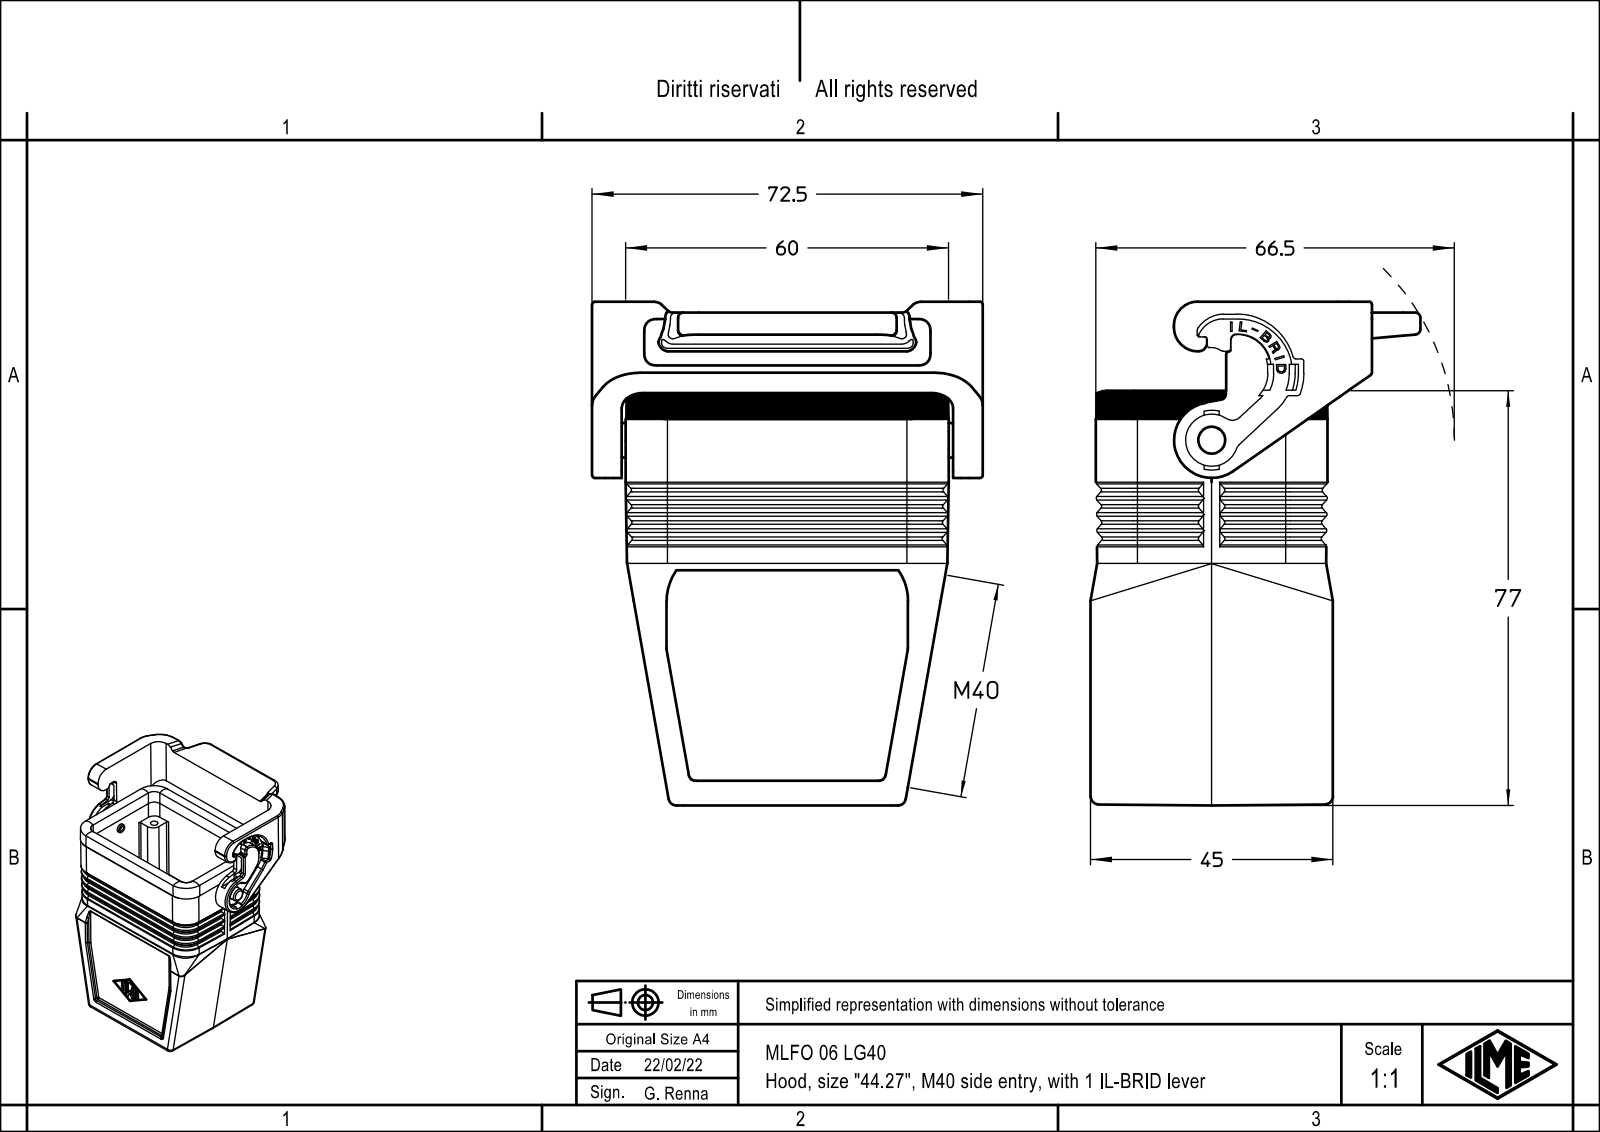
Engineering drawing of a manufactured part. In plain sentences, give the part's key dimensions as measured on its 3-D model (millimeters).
The part is named "MLFO_06_LG40". Its 3-D file was written by "Creo Elements/Direct Modeling 20.1B 02-Apr-2019 (C) Parametric Technology GmbH (AUTOMOTIVE_DESIGN)". It is 1 solid with 977 faces: 589 planar, 255 cylindrical and 133 other. Overall it measures 93.45 by 72.5 by 61.25 millimeters. Its volume is 72 550 cubic millimeters and its surface area 37 855 square millimeters. Round holes: 4 of diameter 2.75, 1 of diameter 38.6. Round bosses or shafts: 1 of diameter 6.8, 1 of diameter 4.8. Partial cylindrical surfaces (rounded edges, fillets, slot ends): 57 of radius 0.5, 43 of radius 1, 16 of radius 1.5, 16 of radius 3, 15 of radius 0.33, 14 of radius 7, 4 of radius 0.3, 4 of radius 2. The main face-to-face distances are 39.25, 3.75, 43, 1, 4.75, 7, 3.65, 35.5, 4.5, 57. The hole center spacings are 27, 44, 51.62.
